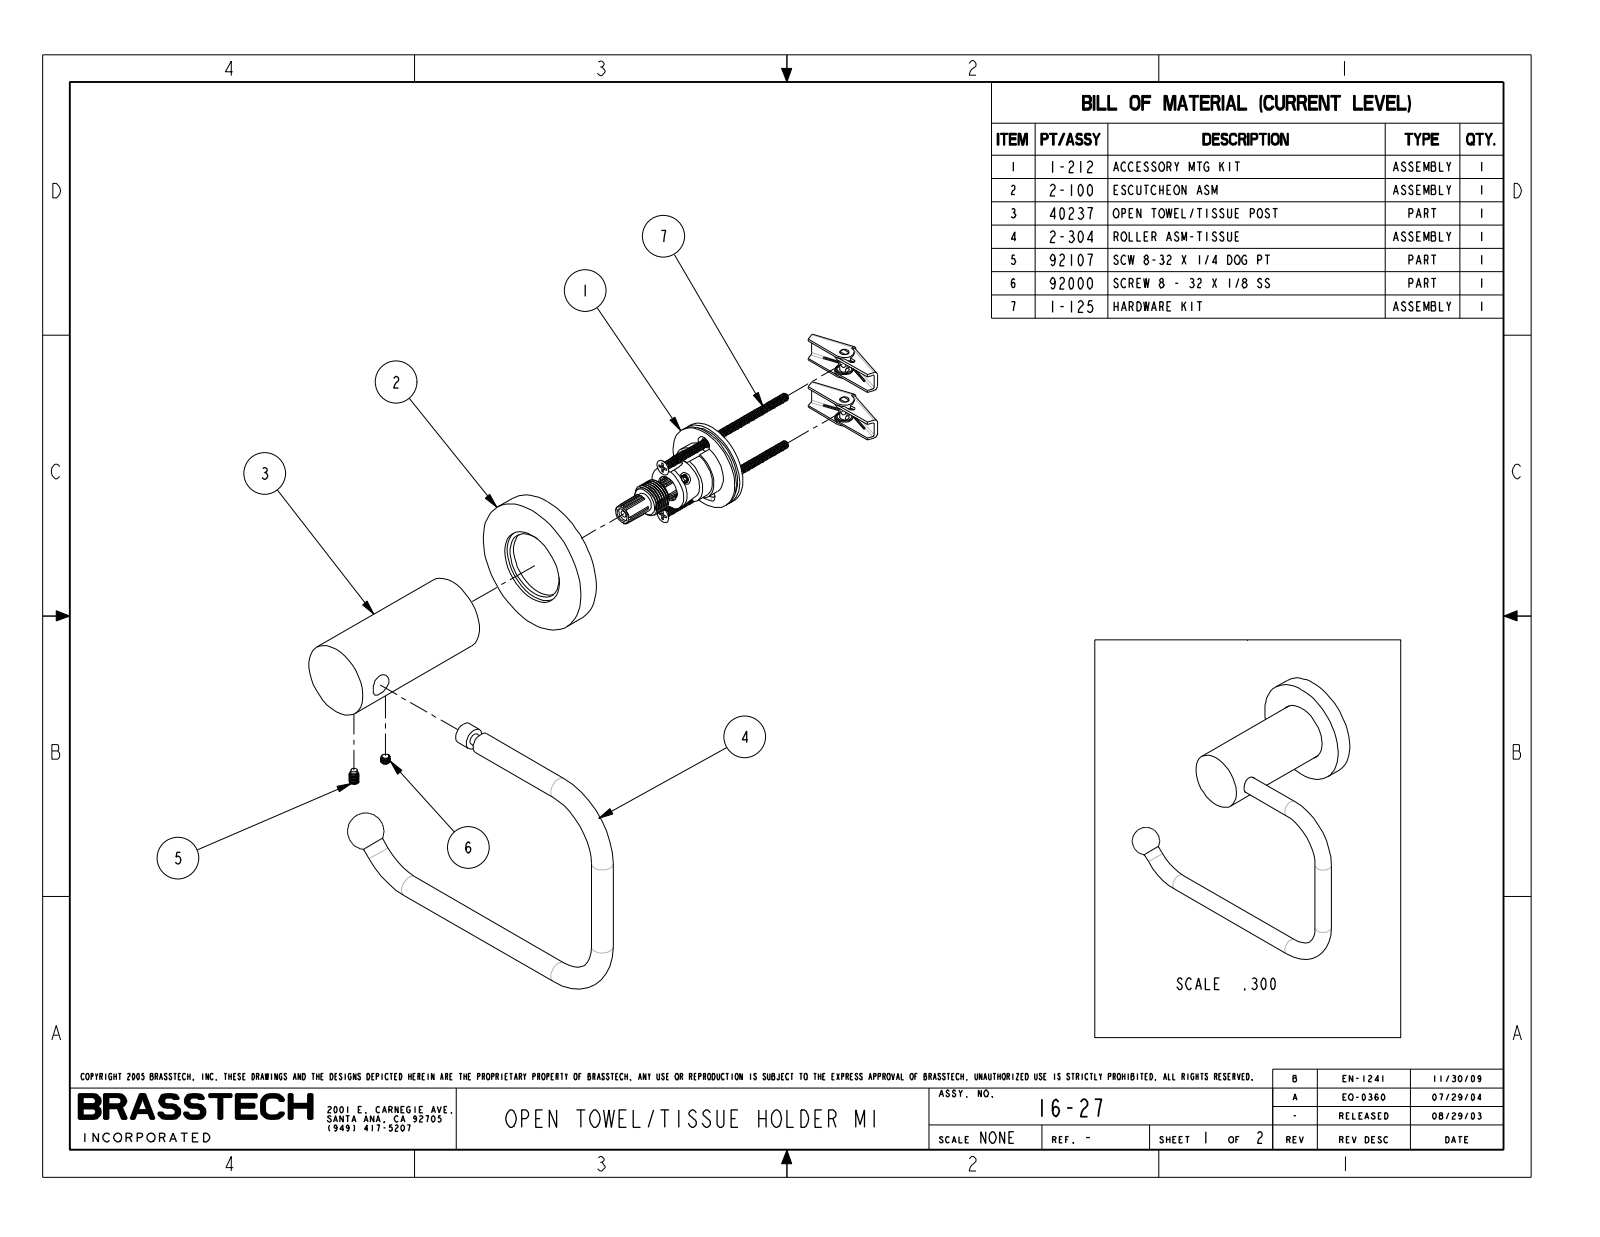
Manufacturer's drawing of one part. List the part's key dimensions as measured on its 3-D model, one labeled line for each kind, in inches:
Part name (STEP PRODUCT): 16-27_SPEC_SW0001
STEP written by: PRO/ENGINEER BY PARAMETRIC TECHNOLOGY CORPORATION, 2009300 (CONFIG_CONTROL_DESIGN)
Units: inches
Bodies: 0 solids, 73 faces (6 planar, 44 cylindrical, 23 other)
Overall size (bounding box): 6.247 × 5.25 × 3.146
Round holes (diameter × count): ⌀0.136 ×1, ⌀0.386 ×1
Round bosses / shafts (diameter × count): ⌀0.375 ×4, ⌀2.375 ×1, ⌀1.313 ×1
Main face-to-face distances: 0.375, 3.145, 2.77
